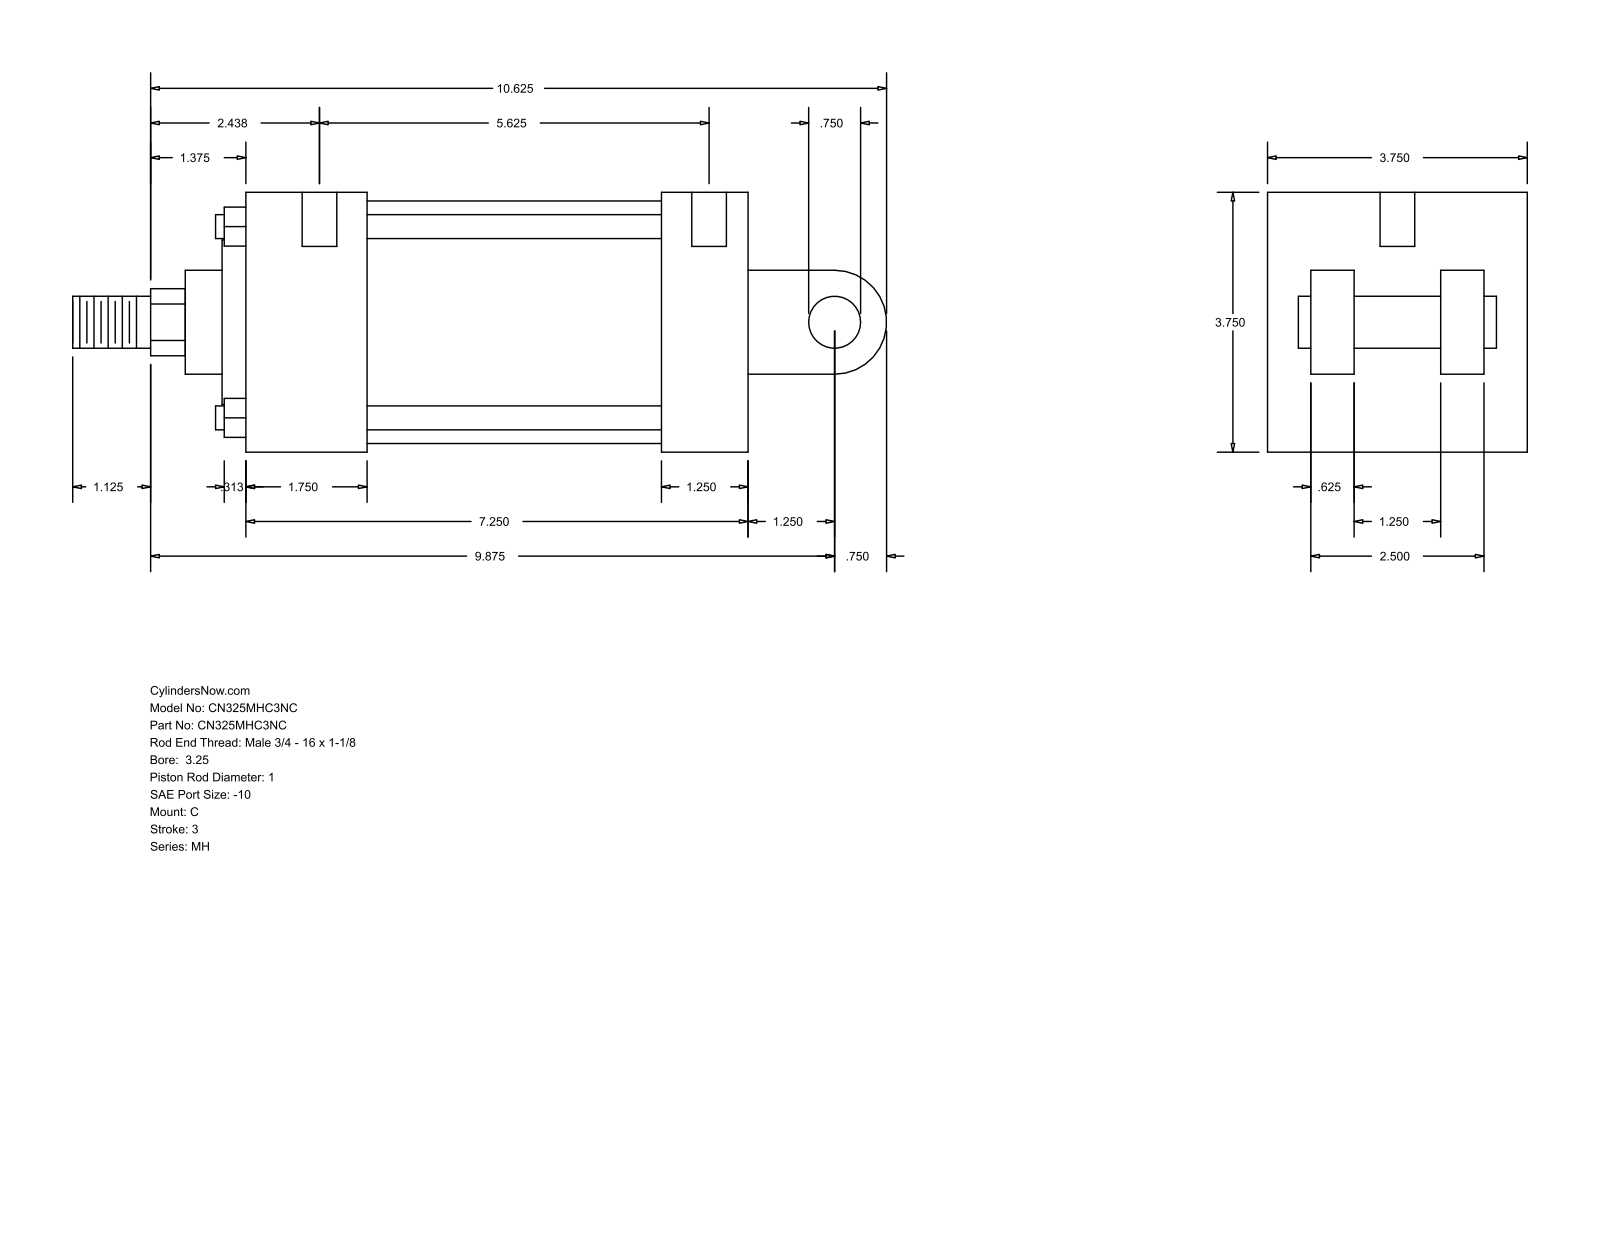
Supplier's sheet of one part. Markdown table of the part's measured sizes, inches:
| quantity | value |
| --- | --- |
| part name | MH_C__0325_1 |
| STEP written by | GSSL Pune (CONFIG_CONTROL_DESIGN) |
| units | inches |
| bodies | 0 solids, 101 faces (71 planar, 30 cylindrical, 0 other) |
| overall size | 11.75 × 3.75 × 3.75 |
| round holes (diameter × count) | 0.219 × 4, 0.5 × 2 |
| round bosses / shafts (diameter × count) | 0.345 × 4, 0.75 × 2, 3.5 × 1, 2.375 × 1, 1.5 × 1, 1 × 1 |
| partial cylindrical surfaces (radius × count) | 0.484 × 1, 0.75 × 1 |
| main face-to-face distances | 3.75, 0.625, 7.25, 2.5, 1.25, 3.125, 1.875, 1.75, 6, 4.25 |
| hole center spacings | 5.875, 0.062, 0.187, 5.625, 5.687, 5.813 |
